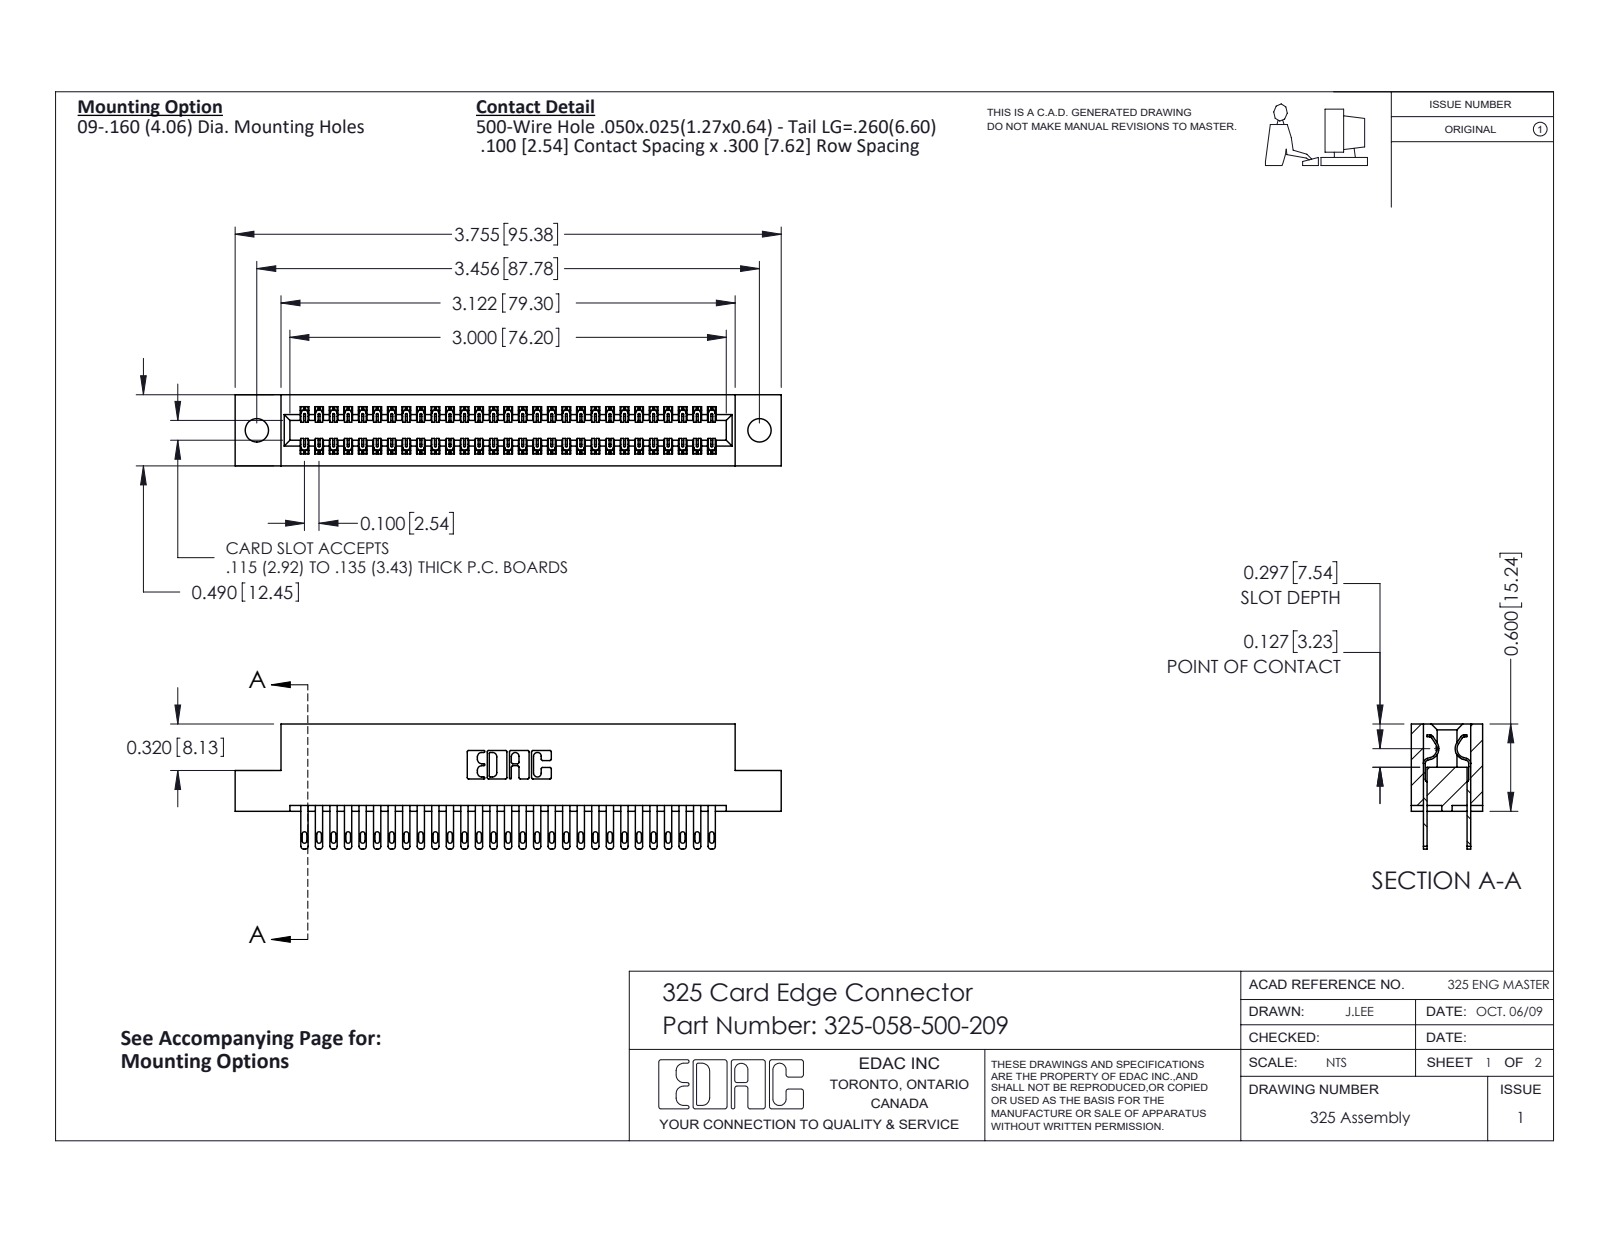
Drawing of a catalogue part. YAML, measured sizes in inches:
part_name: "325-292-001_325-293-100; 325-058-500-209; 325 Part_.160 TH"
step_written_by: "SolidWorks 2016 (CONFIG_CONTROL_DESIGN)"
units: inches
bodies: {solids: 59, faces: 2898, planar: 1810, cylindrical: 1088, other: 0}
overall_size: [3.755, 0.86, 0.49]
volume: 0.741
surface_area: 23.12
round_holes:
  - {diameter: 0.16, count: 2}
partial_cylinders:
  - {radius: 0.006, count: 87}
  - {radius: 0.016, count: 58}
  - {radius: 0.02, count: 58}
  - {radius: 0.01, count: 22}
  - {radius: 0.007, count: 6}
  - {radius: 0.031, count: 6}
  - {radius: 0.026, count: 3}
  - {radius: 0.014, count: 2}
face_to_face_distances: [0.083, 0.407, 0.3, 0.107, 0.383, 0.025, 0.49, 0.325, 0.275, 0.04]
hole_center_spacings: [3.456]
